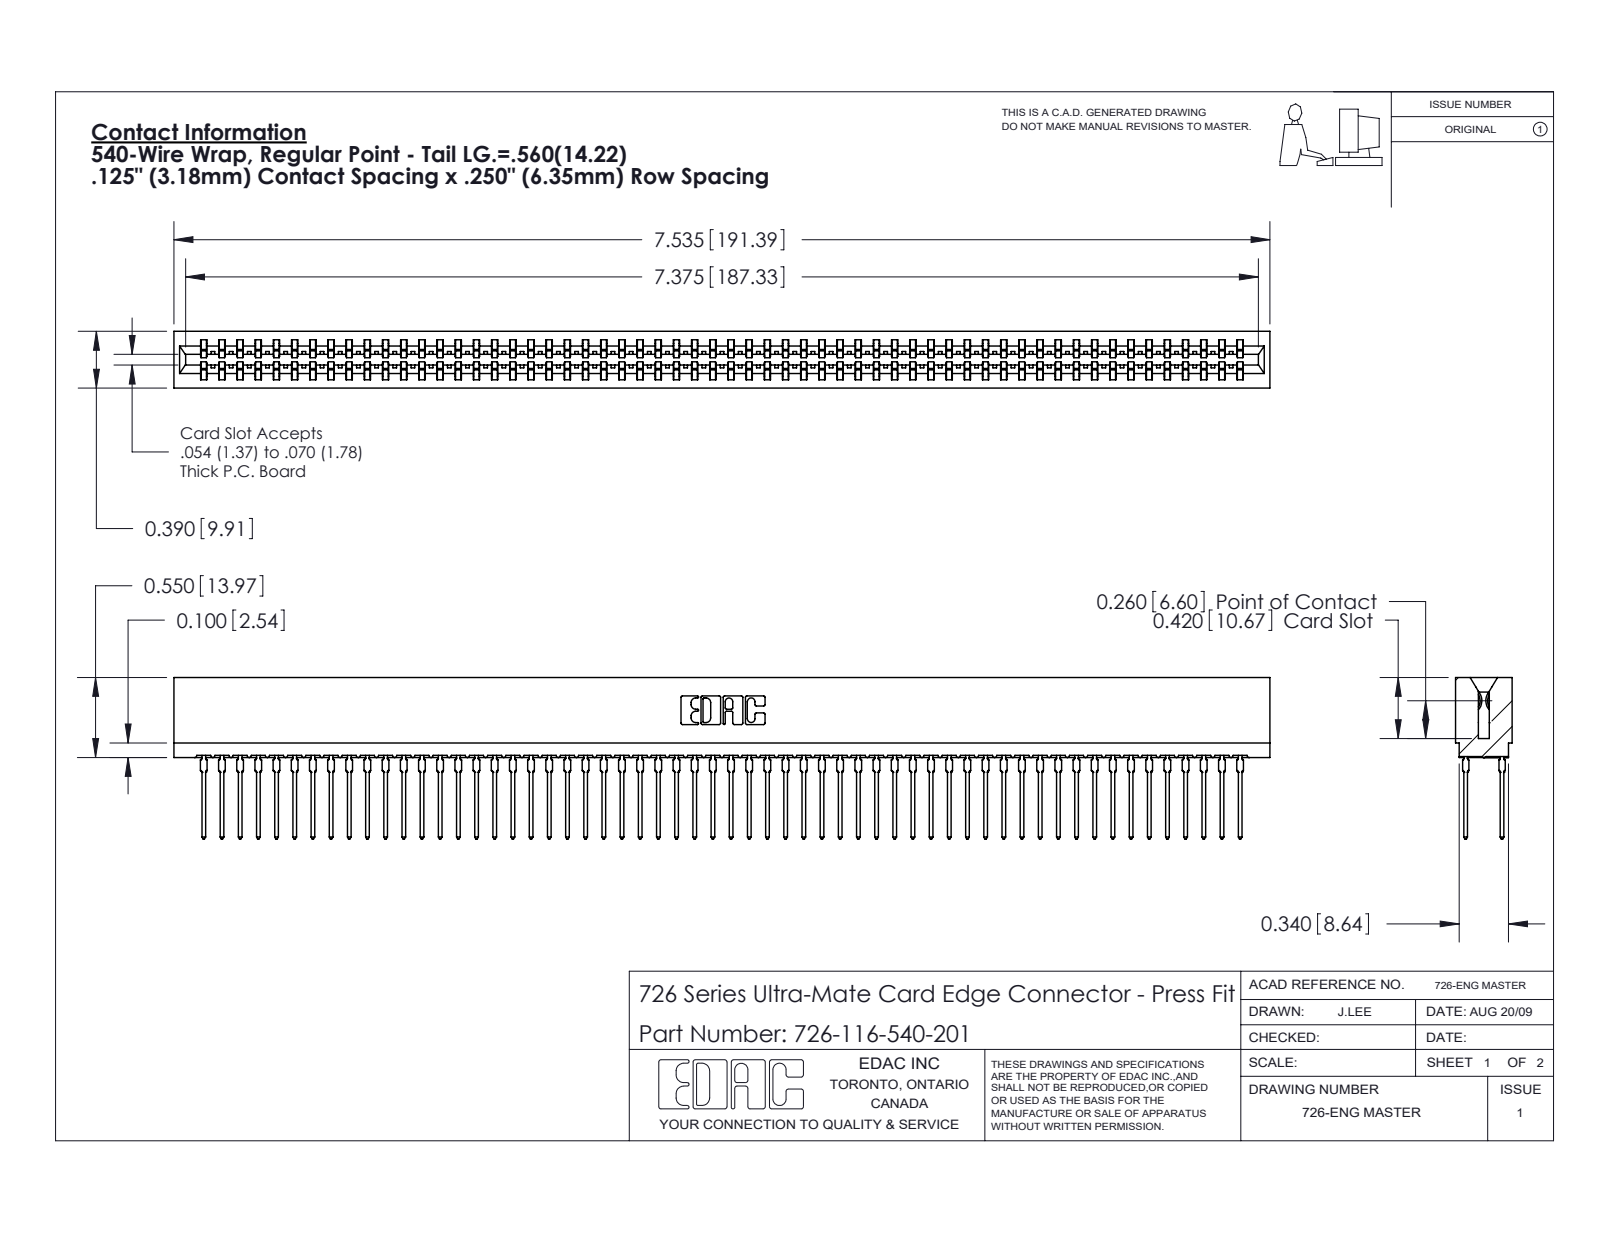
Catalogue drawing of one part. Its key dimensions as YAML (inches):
part_name: "746-292-001_540; 726-116-540-201; 726 Part_.515 Slot Depth - 01"
step_written_by: "SolidWorks 2020 (CONFIG_CONTROL_DESIGN)"
units: inches
bodies: {solids: 117, faces: 10479, planar: 5391, cylindrical: 2072, other: 3016}
overall_size: [7.535, 1.109, 0.39]
volume: 1.092
surface_area: 49.15
partial_cylinders:
  - {radius: 0.021, count: 232}
  - {radius: 0.015, count: 59}
  - {radius: 0.01, count: 22}
  - {radius: 0.005, count: 8}
  - {radius: 0.011, count: 8}
  - {radius: 0.007, count: 6}
  - {radius: 0.031, count: 6}
  - {radius: 0.026, count: 3}
face_to_face_distances: [0.057, 0.333, 0.025, 0.307, 0.39, 0.25, 0.275, 0.083, 0.365, 0.032]
